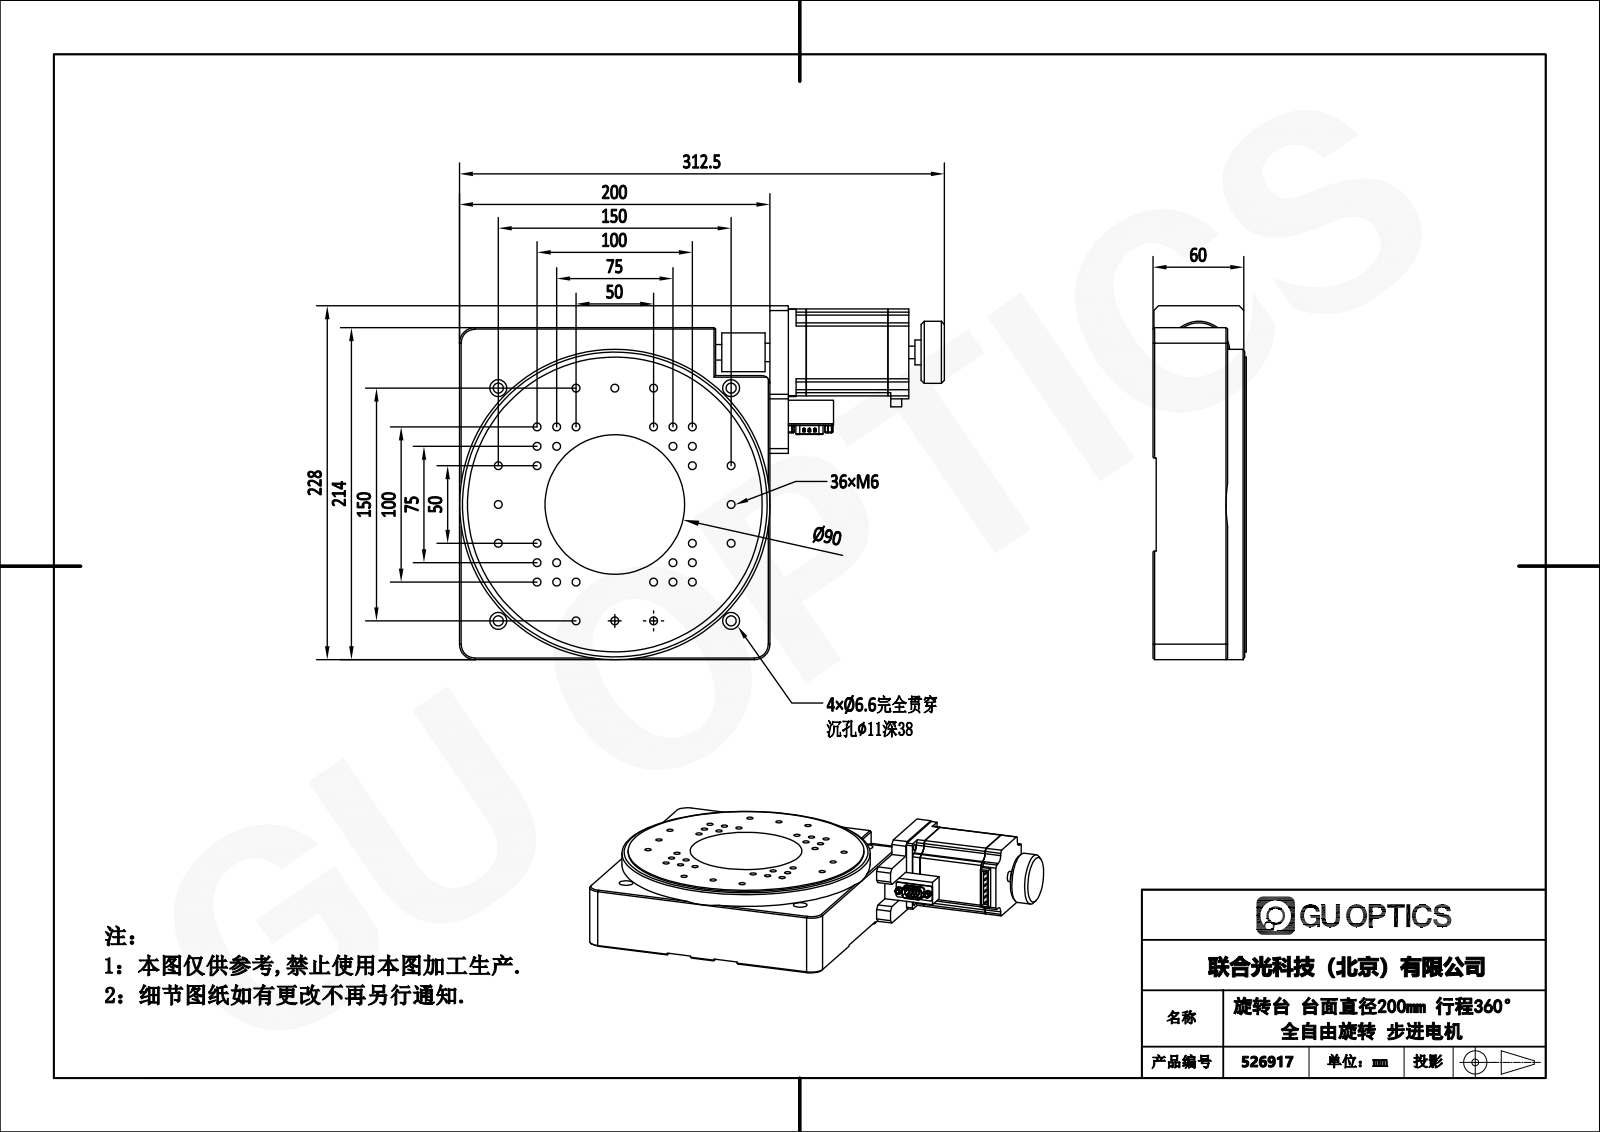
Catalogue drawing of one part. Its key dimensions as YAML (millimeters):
part_name: "FMSR200"
step_written_by: "SolidWorks 2017 (AUTOMOTIVE_DESIGN)"
units: millimeters
bodies: {solids: 7, faces: 1080, planar: 317, cylindrical: 475, other: 288}
overall_size: [312.5, 228, 60]
volume: 2248000
surface_area: 190986
round_holes:
  - {diameter: 5, count: 36}
  - {diameter: 1.1, count: 9}
  - {diameter: 5.1, count: 4}
  - {diameter: 6.6, count: 4}
  - {diameter: 11, count: 4}
  - {diameter: 2.5, count: 2}
  - {diameter: 3.2, count: 2}
  - {diameter: 40, count: 1}
  - {diameter: 90, count: 1}
round_bosses_or_shafts:
  - {diameter: 1, count: 15}
  - {diameter: 1.5, count: 9}
  - {diameter: 3, count: 2}
  - {diameter: 200, count: 1}
  - {diameter: 190, count: 1}
  - {diameter: 38, count: 1}
  - {diameter: 25, count: 1}
  - {diameter: 16, count: 1}
partial_cylinders:
  - {radius: 0.5, count: 36}
  - {radius: 1, count: 16}
  - {radius: 2, count: 14}
  - {radius: 0.4, count: 8}
  - {radius: 1.9, count: 8}
  - {radius: 5, count: 5}
  - {radius: 0.3, count: 4}
  - {radius: 1.3, count: 4}
face_to_face_distances: [60, 12, 58, 2, 48, 46, 200, 214, 1.5, 0.5]
hole_center_spacings: [125, 55.9, 12.5, 62.5, 25, 79.06, 115.24, 88.39]
